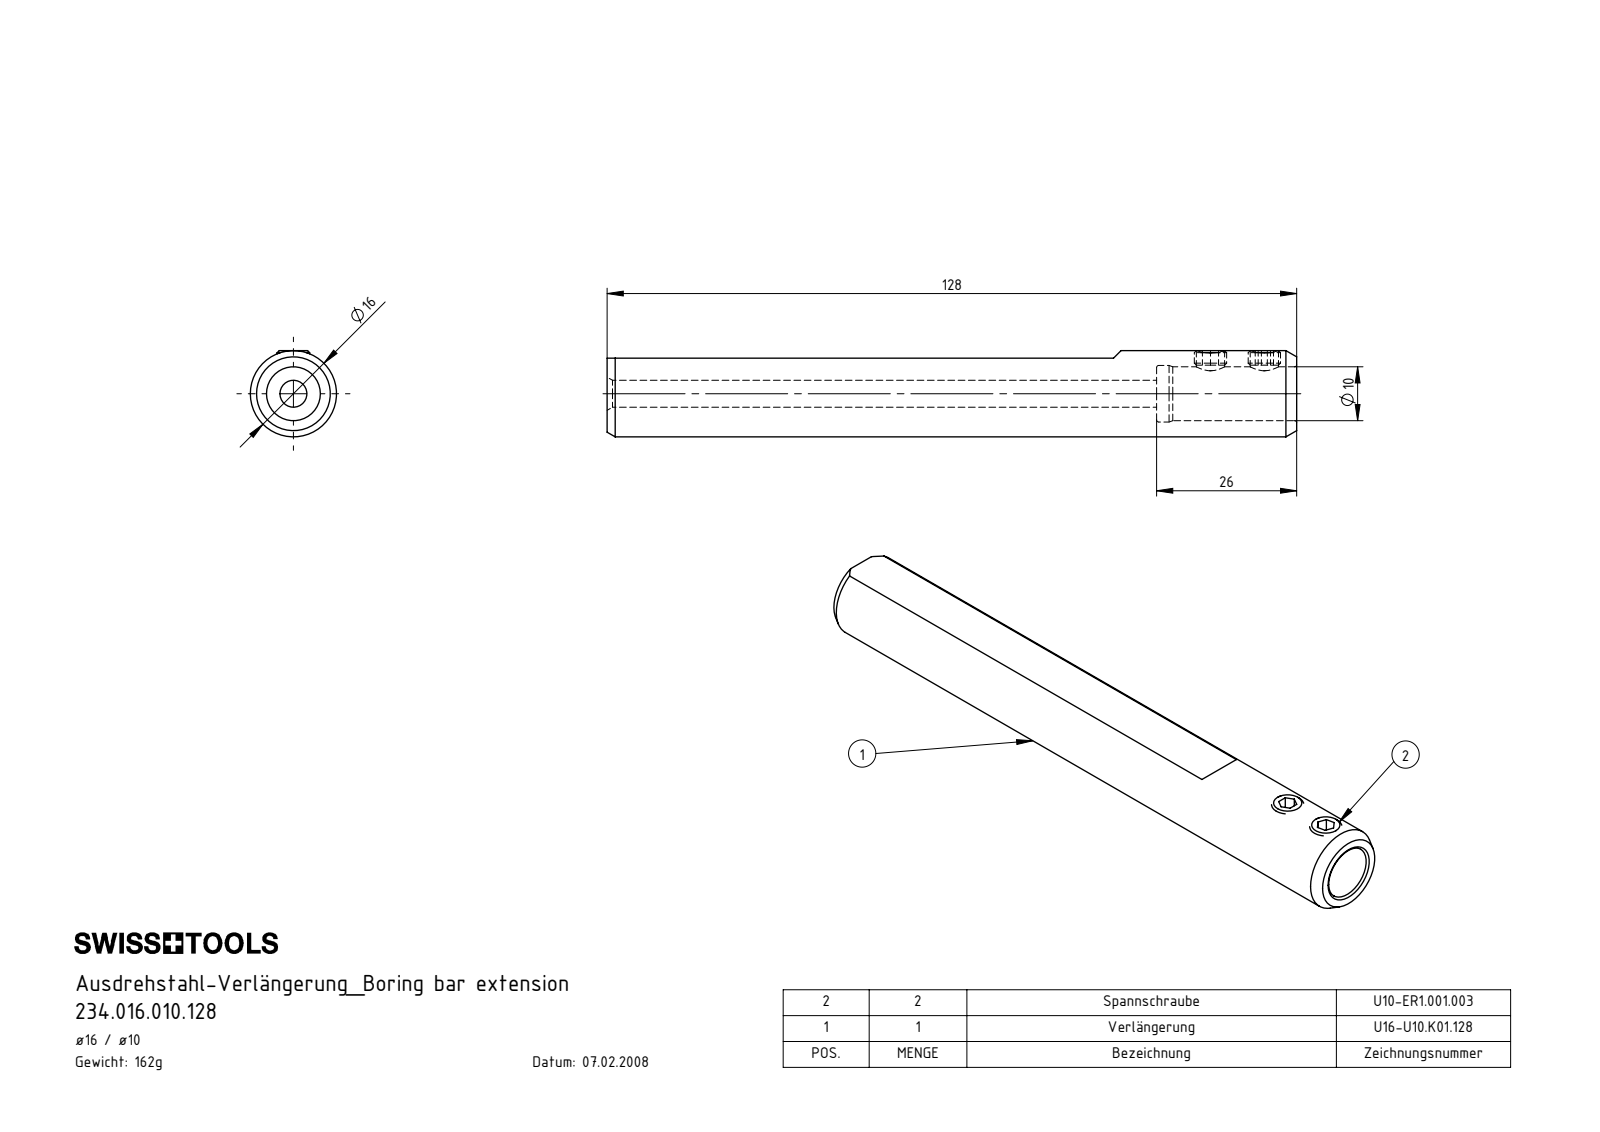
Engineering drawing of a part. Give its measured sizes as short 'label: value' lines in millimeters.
name: U16.U10.K01.128; U16-U10.K01.128_A; U10-ER1.001.003_A
written by: SolidWorks 2017 (AUTOMOTIVE_DESIGN)
unit: mm
bodies: 3 solids, 39 faces (21 planar, 8 cylindrical, 10 other)
size: 128 × 16 × 16
volume: 20 743 mm³; area: 9 316 mm²
holes: 2× ⌀5.25, 1× ⌀5, 1× ⌀10, 1× ⌀10.5
bosses: 2× ⌀6, 1× ⌀16
face distances: 128, 102, 26, 3, 1.3, 2.7, 1.4, 113.5, 11.5, 14.5
hole spacings: 10
